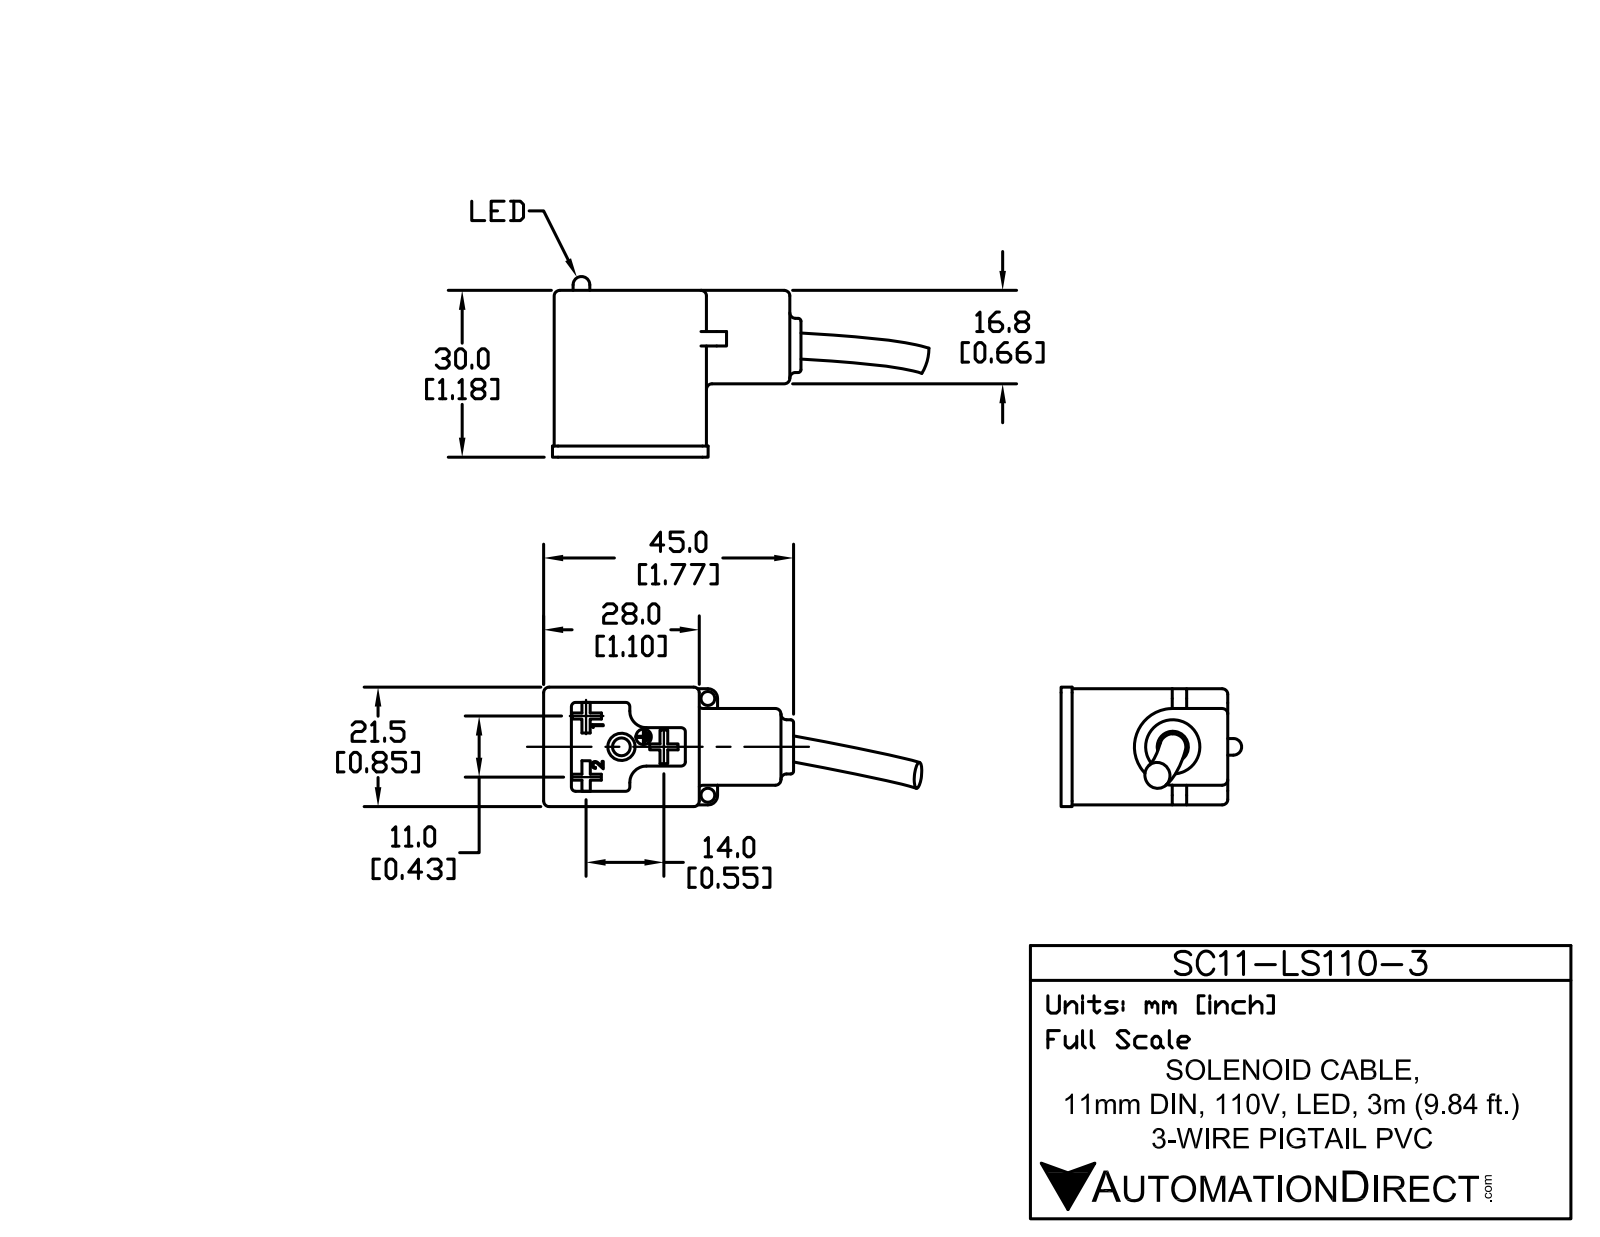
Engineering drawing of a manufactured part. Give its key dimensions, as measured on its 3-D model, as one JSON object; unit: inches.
{"part_name": "SC11-LS110-3", "step_written_by": "SolidWorks 2011 (AUTOMOTIVE_DESIGN)", "units": "inches", "bodies": {"solids": 3, "faces": 205, "planar": 131, "cylindrical": 46, "other": 28}, "overall_size": [2.668, 1.449, 0.846], "volume_in3": 1.22, "surface_area_in2": 10.49, "round_holes": [[0.098, 2], [0.109, 1], [0.126, 1], [0.193, 1], [0.22, 1], [0.26, 1]], "round_bosses_or_shafts": [[0.384, 1], [0.256, 1], [0.118, 1], [0.108, 1]], "partial_cylinders_radius": [[0.039, 19], [0.03, 6], [0.069, 2], [0.118, 2], [0.272, 1]], "face_to_face_distances": [0.823, 1.181, 1.079, 1.102, 0.079, 0.14, 0.683, 1.1, 1.179, 0.543], "hole_center_spacings": [0.559, 0.702, 0.17, 0.685]}
